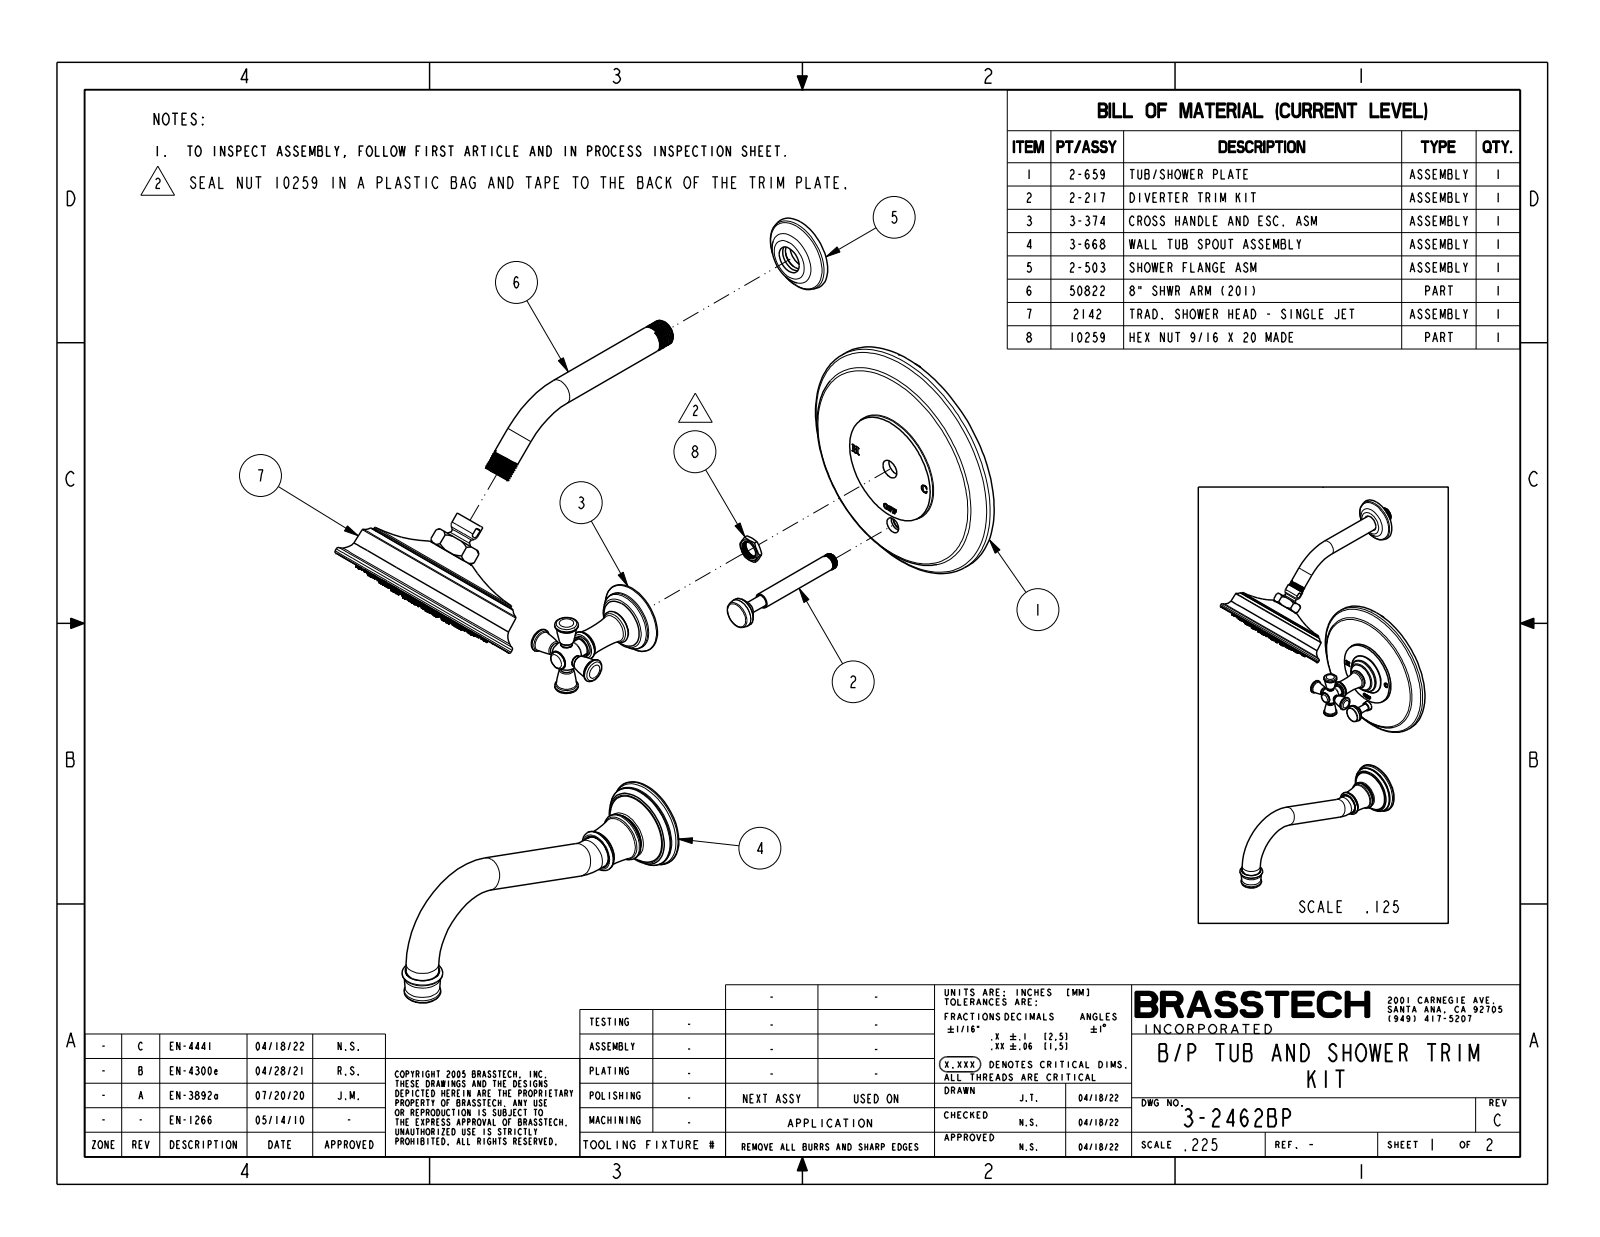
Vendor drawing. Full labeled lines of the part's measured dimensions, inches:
Part name (STEP PRODUCT): 3-2462BP
STEP written by: CREO PARAMETRIC BY PTC INC, 2018400 (CONFIG_CONTROL_DESIGN)
Units: inches
Bodies: 3 solids, 1375 faces (279 planar, 258 cylindrical, 838 other)
Overall size (bounding box): 20.729 × 10.691 × 7.5
Volume: 83.09 in³ · Surface area: 288.7 in²
Round holes (diameter × count): ⌀0.05 ×90, ⌀0.22 ×1, ⌀0.604 ×1, ⌀5.275 ×1
Round bosses / shafts (diameter × count): ⌀1 ×3, ⌀0.9 ×2, ⌀0.813 ×2, ⌀0.72 ×2, ⌀0.36 ×2, ⌀7.5 ×1, ⌀6.2 ×1, ⌀5.22 ×1
Main face-to-face distances: 0.625, 0.75, 0.125, 0.48, 0.145, 0.27, 1.014, 1.897, 1.417, 1.272
Hole centre spacings: 2.27, 0.48, 1.84, 0.952, 1.84, 1.408, 2.24, 2.602
